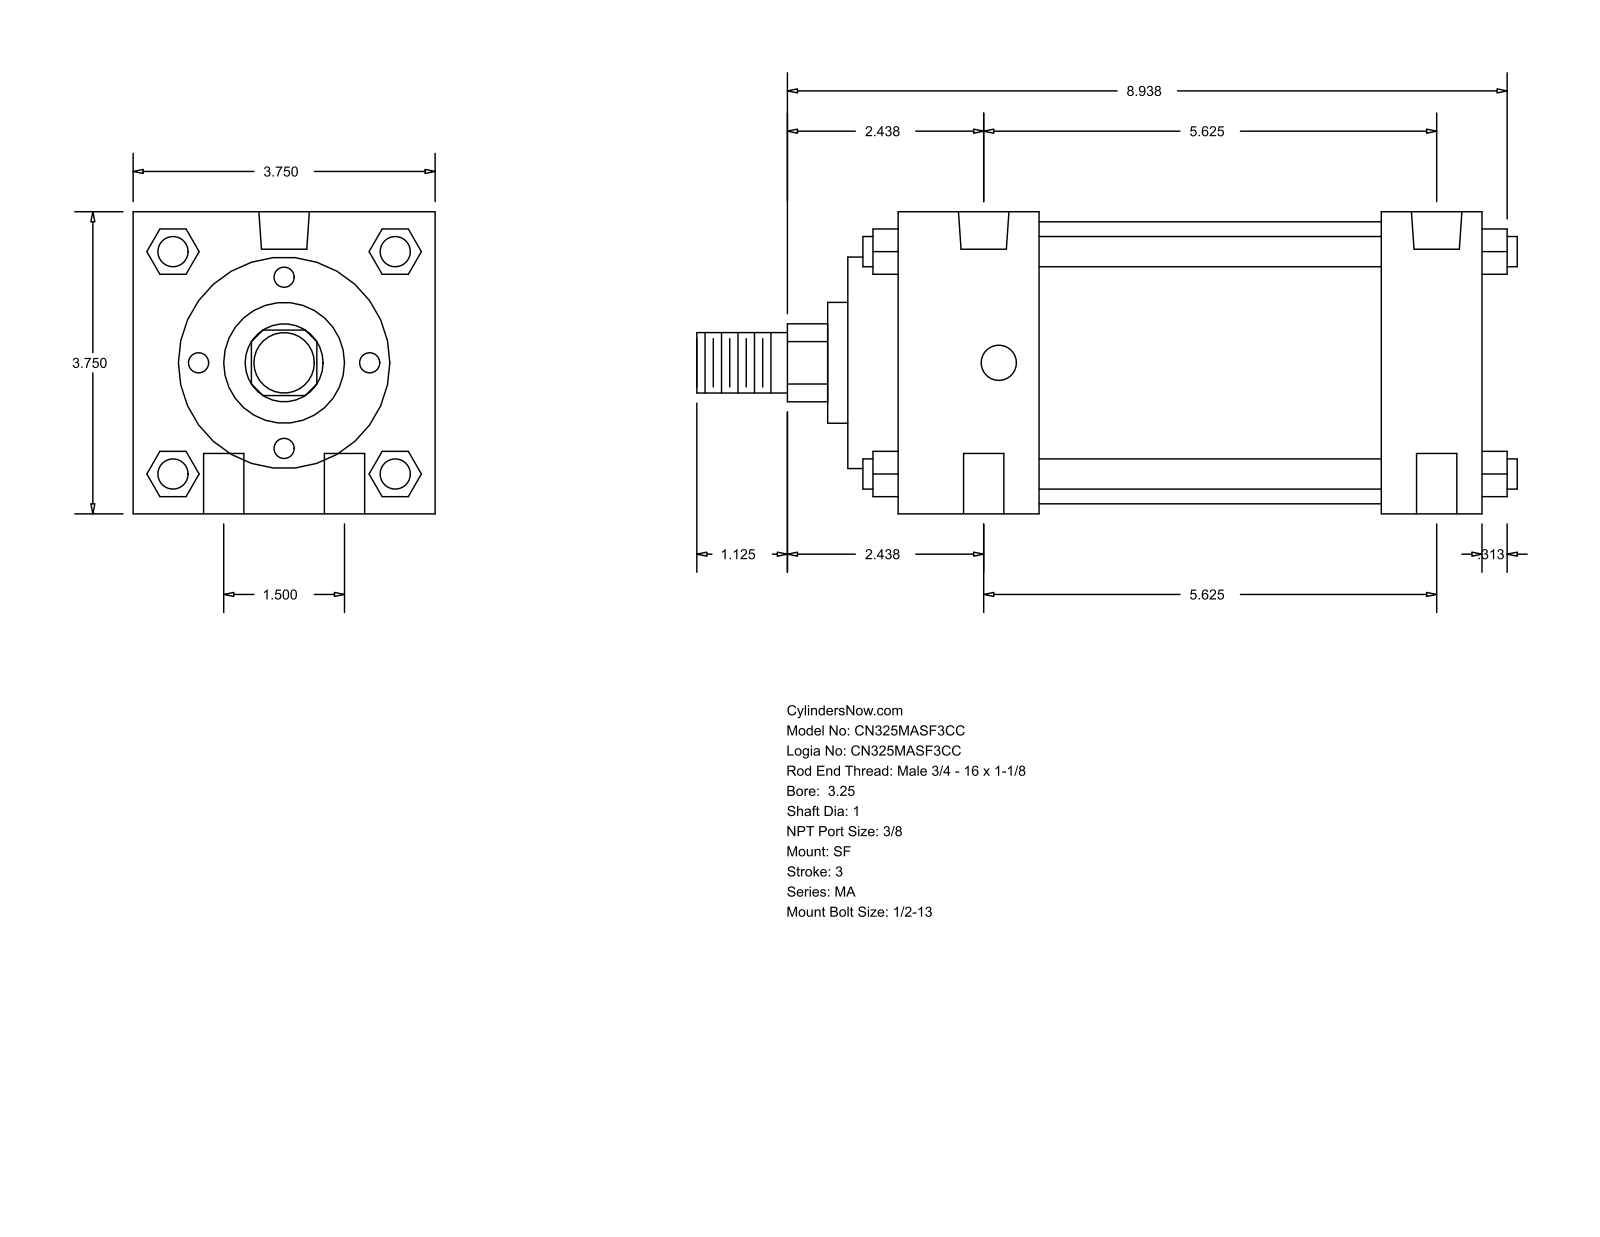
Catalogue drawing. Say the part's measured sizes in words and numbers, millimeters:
The part is named "MA_SF__0325_1". Its 3-D file was written by "GSSL Pune (CONFIG_CONTROL_DESIGN)". It is 0 solids with 126 faces: 95 planar, 31 cylindrical and 0 other. Overall it measures 258.76 by 95.25 by 95.25 millimeters. Round holes: 4 of diameter 12.7, 2 of diameter 11.11, 2 of diameter 15.93. Round bosses or shafts: 4 of diameter 9.53, 1 of diameter 88.9, 1 of diameter 66.67, 1 of diameter 38.1, 1 of diameter 25.4, 1 of diameter 19.05. Partial cylindrical surfaces (rounded edges, fillets, slot ends): 1 of radius 12.29. The main face-to-face distances are 95.24, 184.15, 200.02, 152.4, 31.75, 44.46, 107.94, 139.69, 15.87, 60.33. The hole center spacings are 19.05, 144.14, 142.88, 38.1, 147.87, 133.36.
